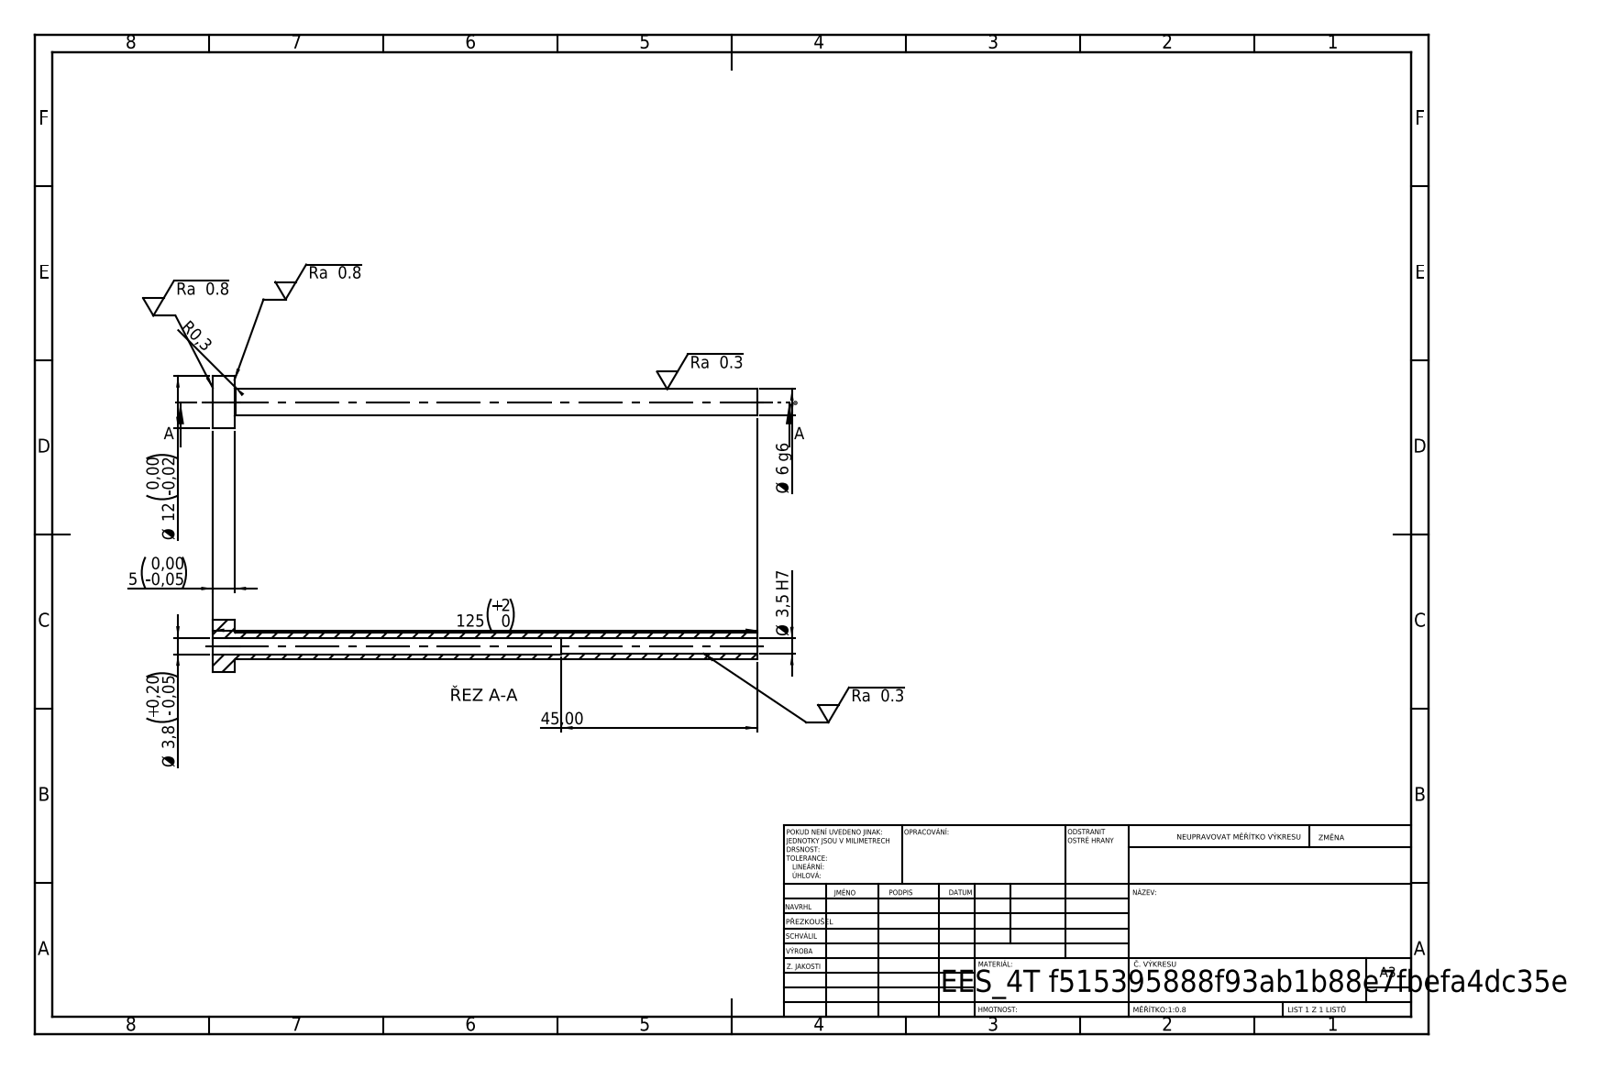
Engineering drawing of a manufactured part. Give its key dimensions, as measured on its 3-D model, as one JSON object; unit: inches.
{"step_written_by": "SolidWorks 2019 (CONFIG_CONTROL_DESIGN)", "units": "inches", "bodies": {"solids": 1, "faces": 14, "planar": 4, "cylindrical": 8, "other": 2}, "overall_size": [4.921, 0.472, 0.472], "volume_in3": 0.16, "surface_area_in2": 6.363, "round_holes": [[0.138, 1], [0.15, 1]], "round_bosses_or_shafts": [[0.472, 1], [0.236, 1]], "face_to_face_distances": [0.197, 4.921, 4.724, 3.15, 2.953, 1.772]}
